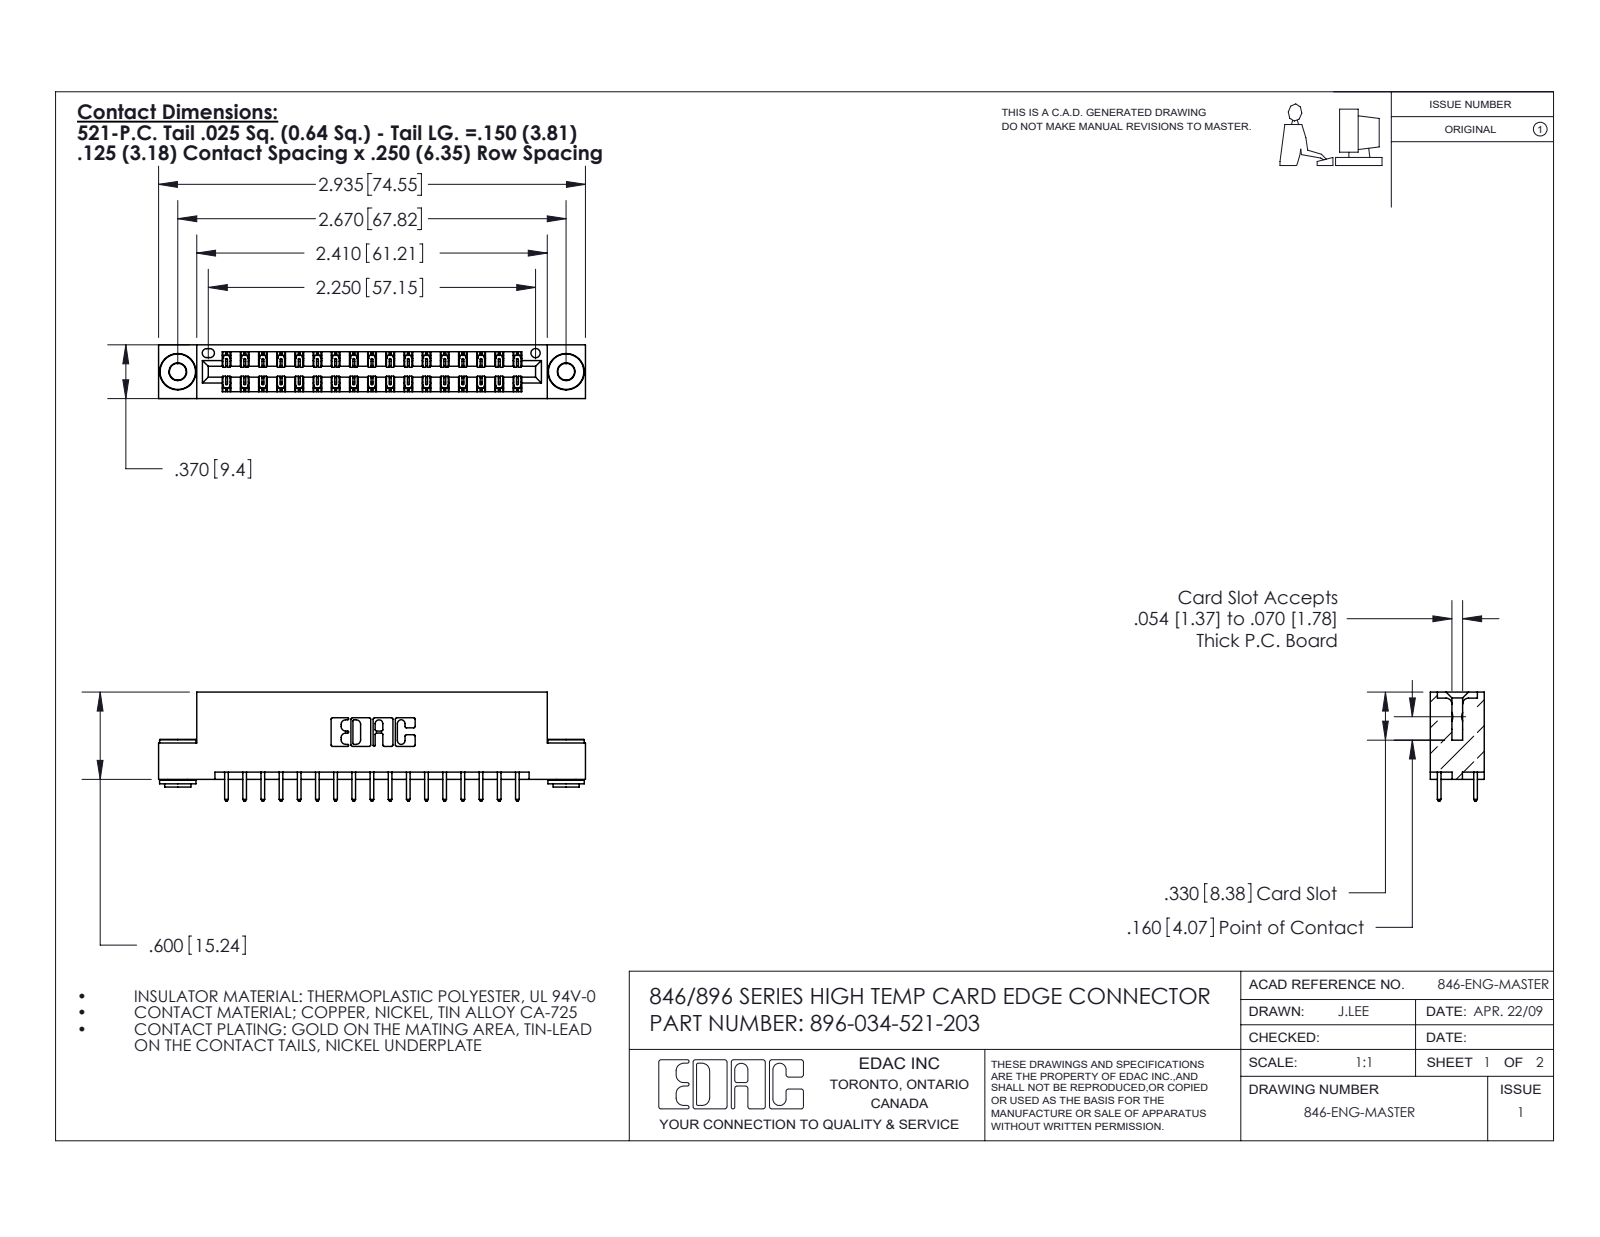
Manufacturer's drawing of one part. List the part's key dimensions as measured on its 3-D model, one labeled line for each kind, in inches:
Part name (STEP PRODUCT): 346 Part_Flush Mounting Lugs - 0.156 Dia-TH; 396-034-521-203; 345-292-001_345-293-121; 345-250-002_345-250-002-102
STEP written by: SolidWorks 2016 (CONFIG_CONTROL_DESIGN)
Units: inches
Bodies: 37 solids, 1928 faces (1276 planar, 644 cylindrical, 8 other)
Overall size (bounding box): 2.935 × 0.75 × 0.37
Volume: 0.432 in³ · Surface area: 14.66 in²
Round holes (diameter × count): ⌀0.116 ×2, ⌀0.156 ×2, ⌀0.064 ×1
Round bosses / shafts (diameter × count): ⌀0.25 ×2, ⌀0.18 ×2, ⌀0.136 ×2
Partial cylindrical surfaces — rounded edges, fillets, slot ends (radius × count): R0.006 ×51, R0.01 ×34, R0.01 ×22, R0.007 ×6, R0.031 ×6, R0.026 ×3, R0.014 ×2, R0.022 ×2
Main face-to-face distances: 0.048, 0.322, 0.25, 0.37, 0.025, 0.072, 0.298, 0.275, 0.148, 0.222
Hole centre spacings: 0.246, 2.463, 2.67
